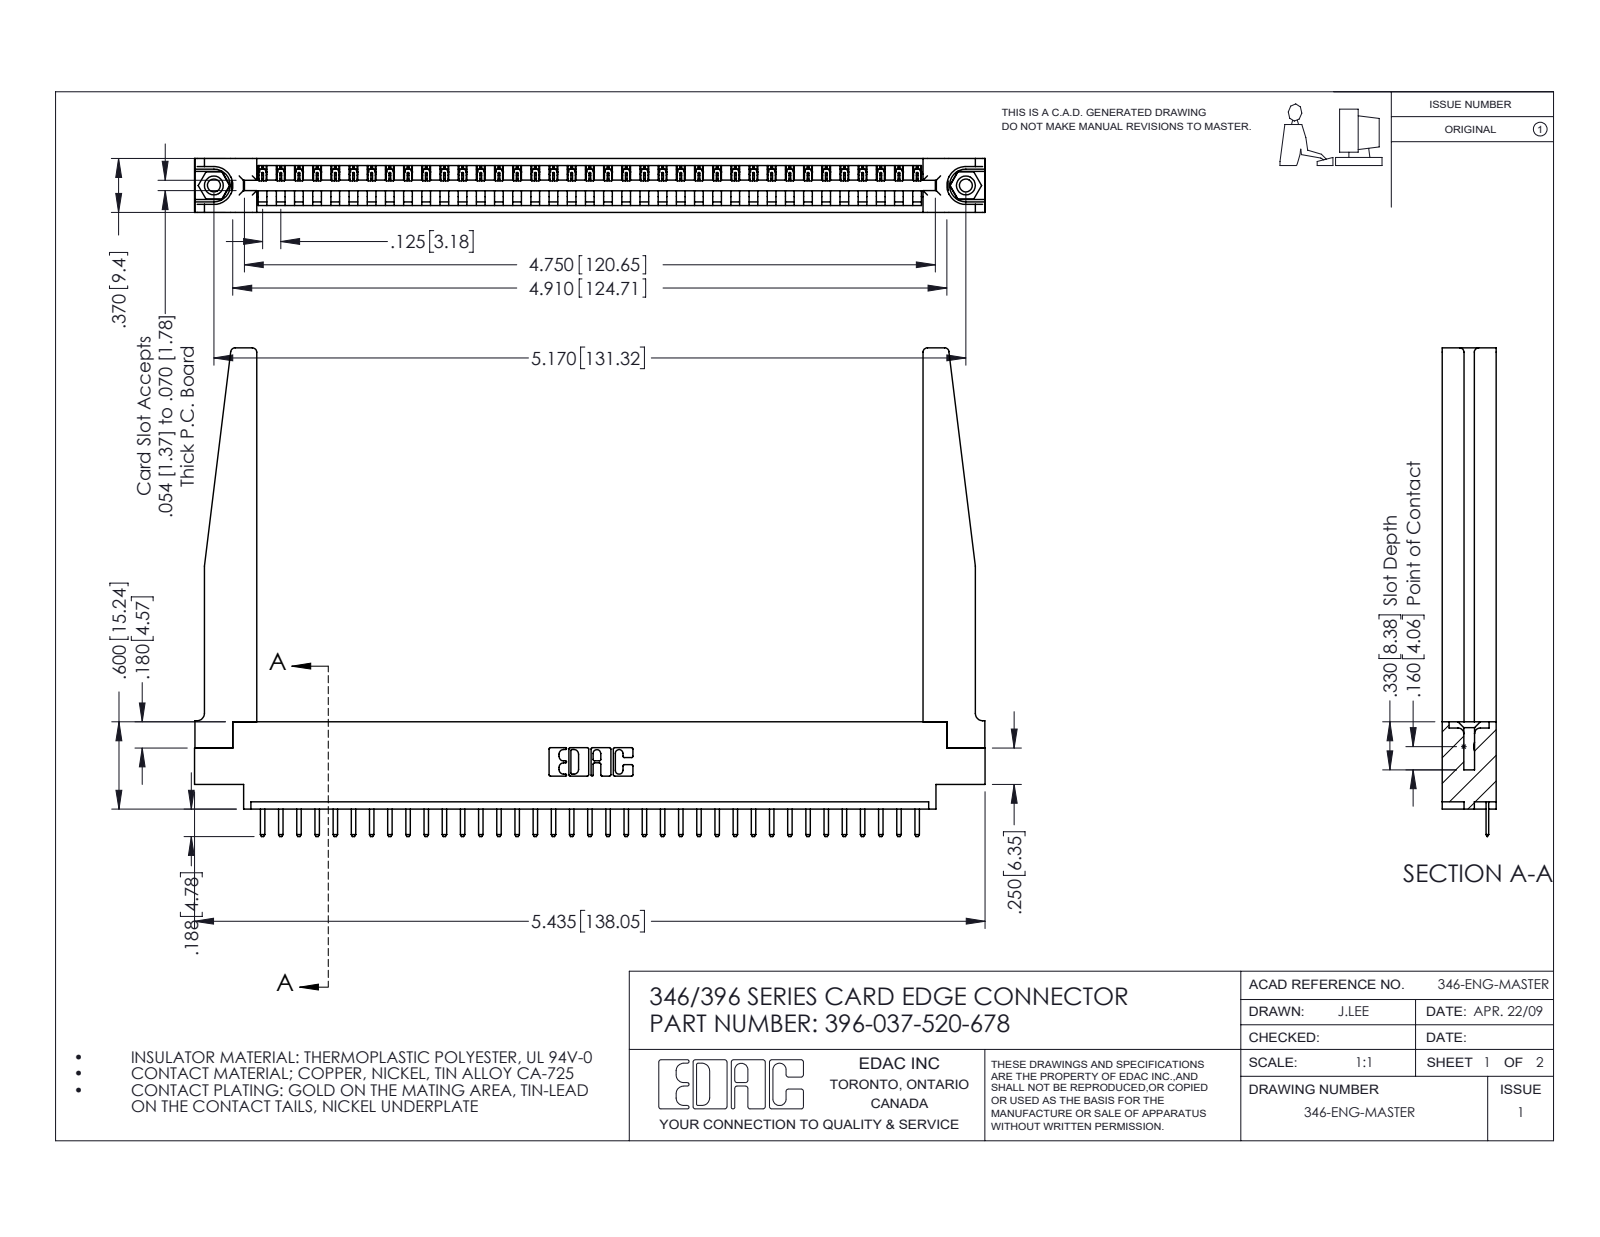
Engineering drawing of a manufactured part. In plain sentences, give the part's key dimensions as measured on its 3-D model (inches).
The part is named "345-250-001_345-250-001-102; 396-037-520-678; 346 Part_0.170 Offset - 0.156 Dia-TH; 345-292-001_345-293-120 (+1 more)". Its 3-D file was written by "SolidWorks 2016 (CONFIG_CONTROL_DESIGN)". It is 42 solids with 2654 faces: 1776 planar, 826 cylindrical and 52 other. Overall it measures 5.435 by 3.358 by 0.37 inches. Its volume is 1.21 cubic inches and its surface area 34.78 square inches. Round holes: 2 of diameter 0.089, 2 of diameter 0.125, 2 of diameter 0.156, 1 of diameter 0.064. Round bosses or shafts: 2 of diameter 0.155. Partial cylindrical surfaces (rounded edges, fillets, slot ends): 76 of radius 0.01, 74 of radius 0.006, 22 of radius 0.01, 8 of radius 0.03, 6 of radius 0.007, 6 of radius 0.031, 3 of radius 0.026, 2 of radius 0.031. The main face-to-face distances are 0.37, 0.048, 0.322, 0.148, 0.072, 0.15, 0.25, 0.222, 0.1, 0.174. The hole center spacings are 0.246, 4.961, 5.17.
